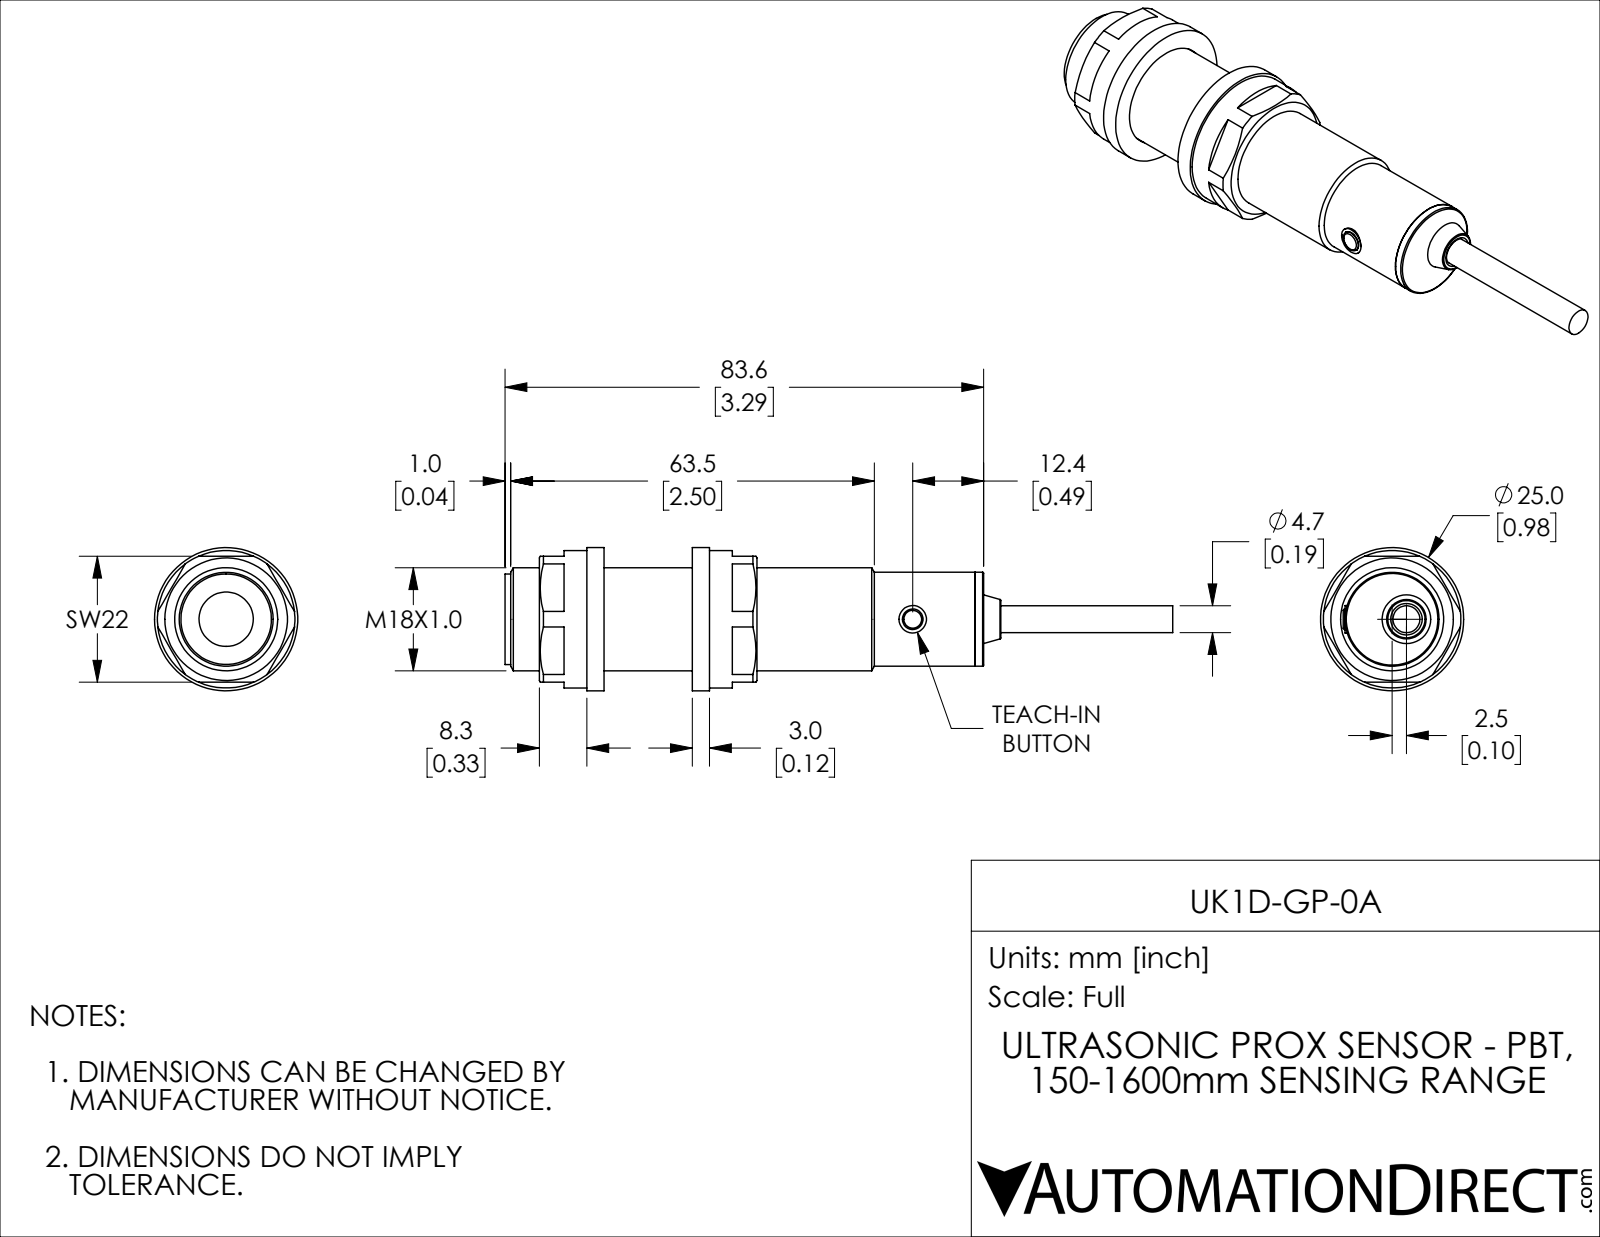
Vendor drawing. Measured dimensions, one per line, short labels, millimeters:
name: UK1D-GP-0A
written by: SolidWorks 2018 (AUTOMOTIVE_DESIGN)
unit: mm
bodies: 10 solids, 107 faces (49 planar, 40 cylindrical, 18 other)
size: 116.6 × 25 × 25
volume: 25 220 mm³; area: 11 419 mm²
holes: 2× ⌀4.7, 1× ⌀3.6, 1× ⌀9.5, 1× ⌀18, 1× ⌀18.2
bosses: 1× ⌀25, 1× ⌀24, 1× ⌀16.4, 1× ⌀15.8, 1× ⌀5.4, 1× ⌀4.8
face distances: 3, 18.4, 21.4, 67.8, 46.4, 13.3, 34.7, 81.1, 16.3, 64.8
hole spacings: 2.5
